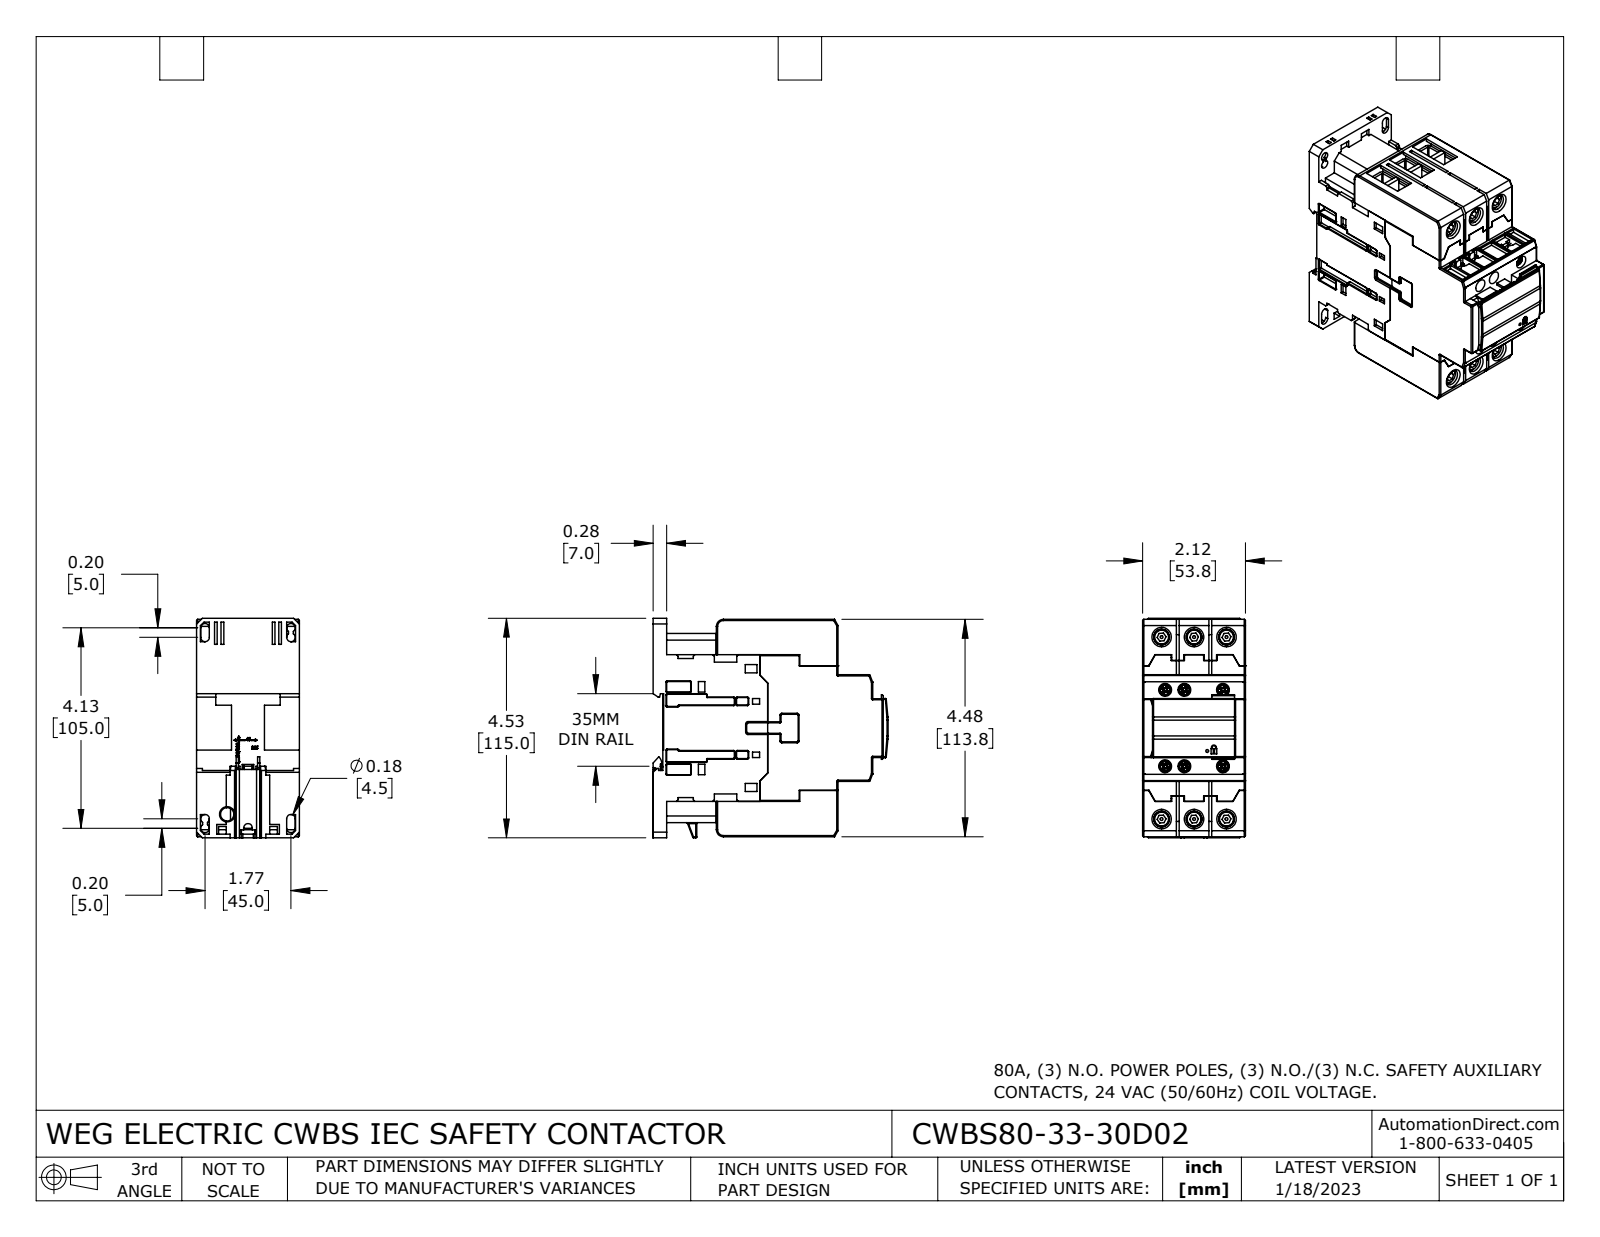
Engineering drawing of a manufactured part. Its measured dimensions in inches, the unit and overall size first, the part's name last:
Units: inches
Overall size (bounding box): 4.846 × 4.528 × 2.118
Round holes (diameter × count): ⌀0.124 ×6, ⌀0.197 ×6, ⌀0.264 ×6, ⌀0.323 ×6, ⌀0.177 ×4, ⌀0.125 ×2, ⌀0.276 ×2, ⌀0.059 ×1
Round bosses / shafts (diameter × count): ⌀0.343 ×6, ⌀0.236 ×6, ⌀0.135 ×6
Partial cylindrical surfaces — rounded edges, fillets, slot ends (radius × count): R0.02 ×89, R0.012 ×69, R0.004 ×48, R0.024 ×42, R0.079 ×18, R0.089 ×5, R0.039 ×3, R0.059 ×3
Main face-to-face distances: 0.059, 2.118, 0.669, 0.728, 3.024, 3.752, 0.108, 0.217, 3.811, 0.098
Hole centre spacings: 0.669, 1.091, 1.241, 1.669, 2.665, 2.73, 2.949, 3.811
Volume: 33.67 in³ · Surface area: 209.3 in²
Bodies: 37 solids, 2637 faces (1669 planar, 550 cylindrical, 418 other)
Part name (STEP PRODUCT): CWBS80-33-30D02
STEP written by: SolidWorks 2021 (CONFIG_CONTROL_DESIGN)
